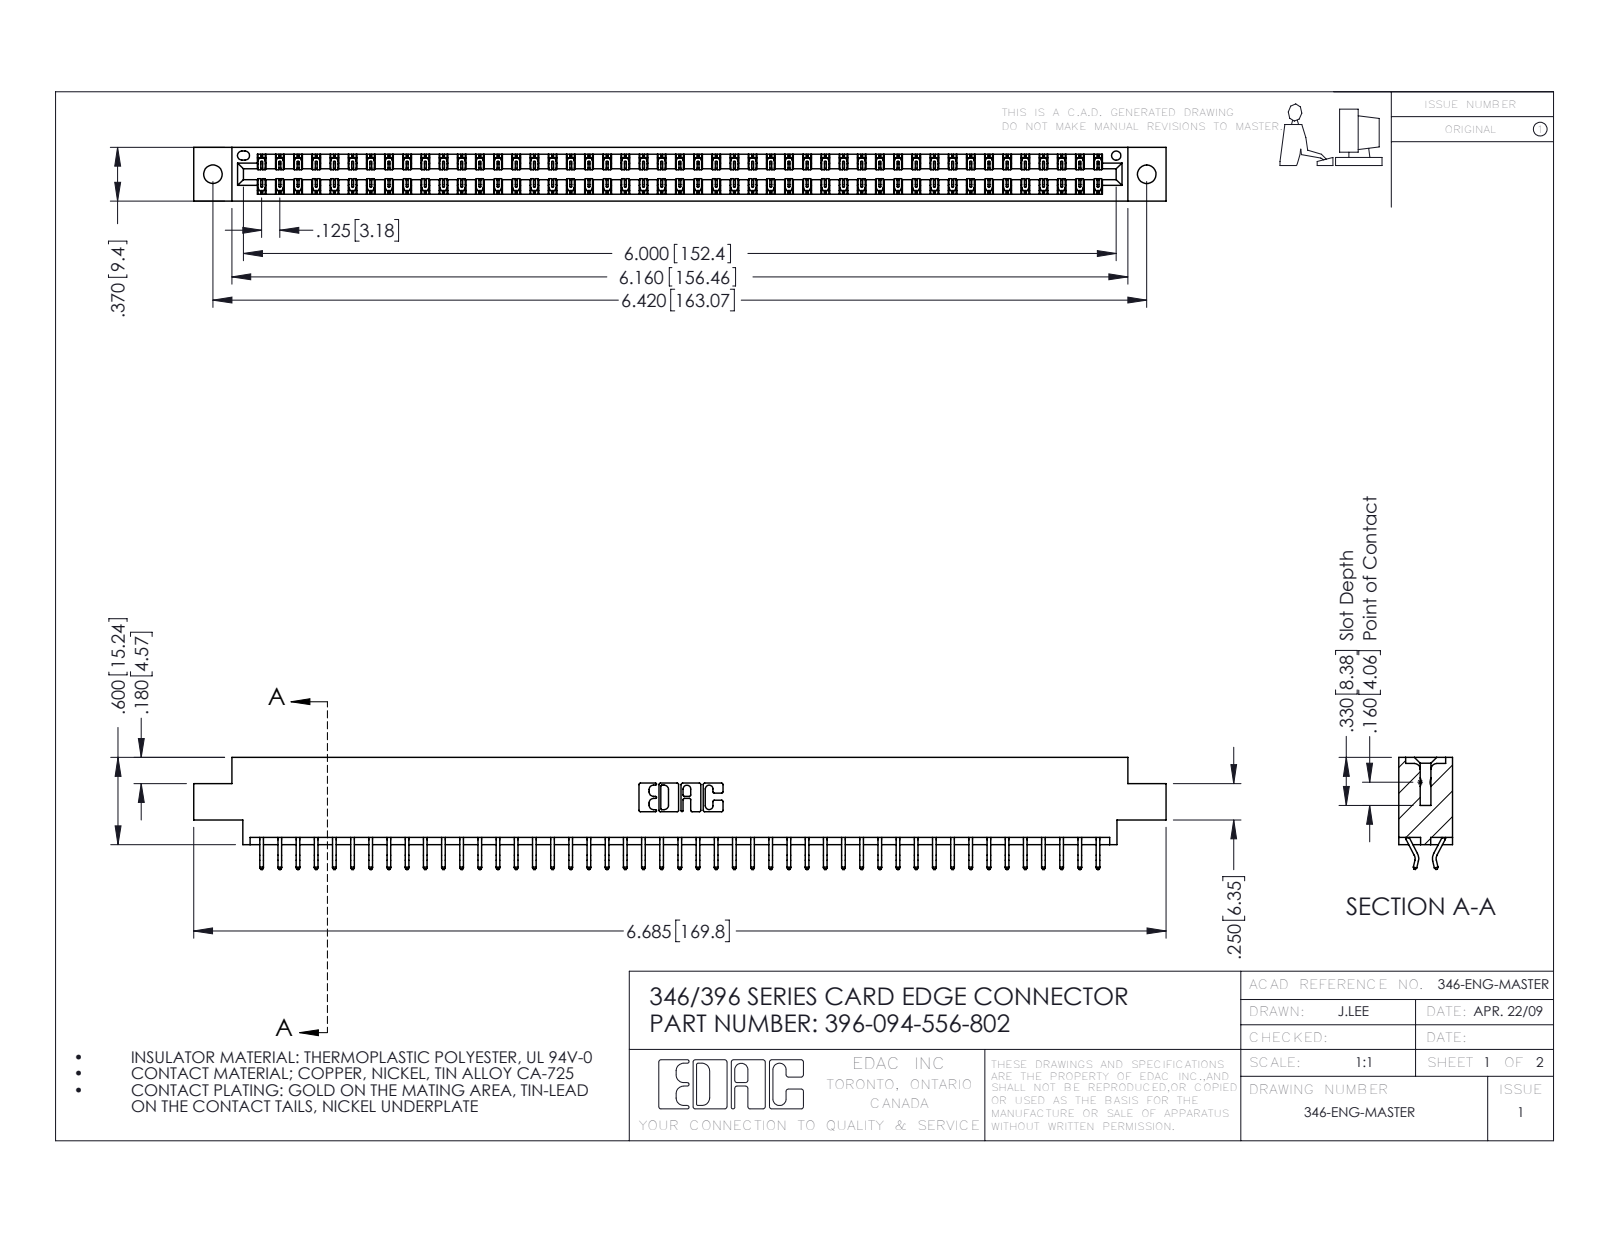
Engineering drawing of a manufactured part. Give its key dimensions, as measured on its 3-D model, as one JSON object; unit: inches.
{"part_name": "345-292-001_556 Tail; 346 Part_0.170 Offset - 0.128 Dia; 396-094-556-802", "step_written_by": "SolidWorks 2016 (CONFIG_CONTROL_DESIGN)", "units": "inches", "bodies": {"solids": 95, "faces": 5578, "planar": 3746, "cylindrical": 1832, "other": 0}, "overall_size": [6.685, 0.77, 0.37], "volume_in3": 1.001, "surface_area_in2": 34.79, "round_holes": [[0.128, 2], [0.064, 1]], "partial_cylinders_radius": [[0.006, 141], [0.01, 22], [0.007, 6], [0.031, 6], [0.026, 3], [0.01, 2], [0.014, 2], [0.022, 2]], "face_to_face_distances": [0.048, 0.322, 0.37, 0.25, 0.025, 0.072, 0.298, 0.275, 0.148, 0.222], "hole_center_spacings": [0.246, 6.211, 6.42]}
